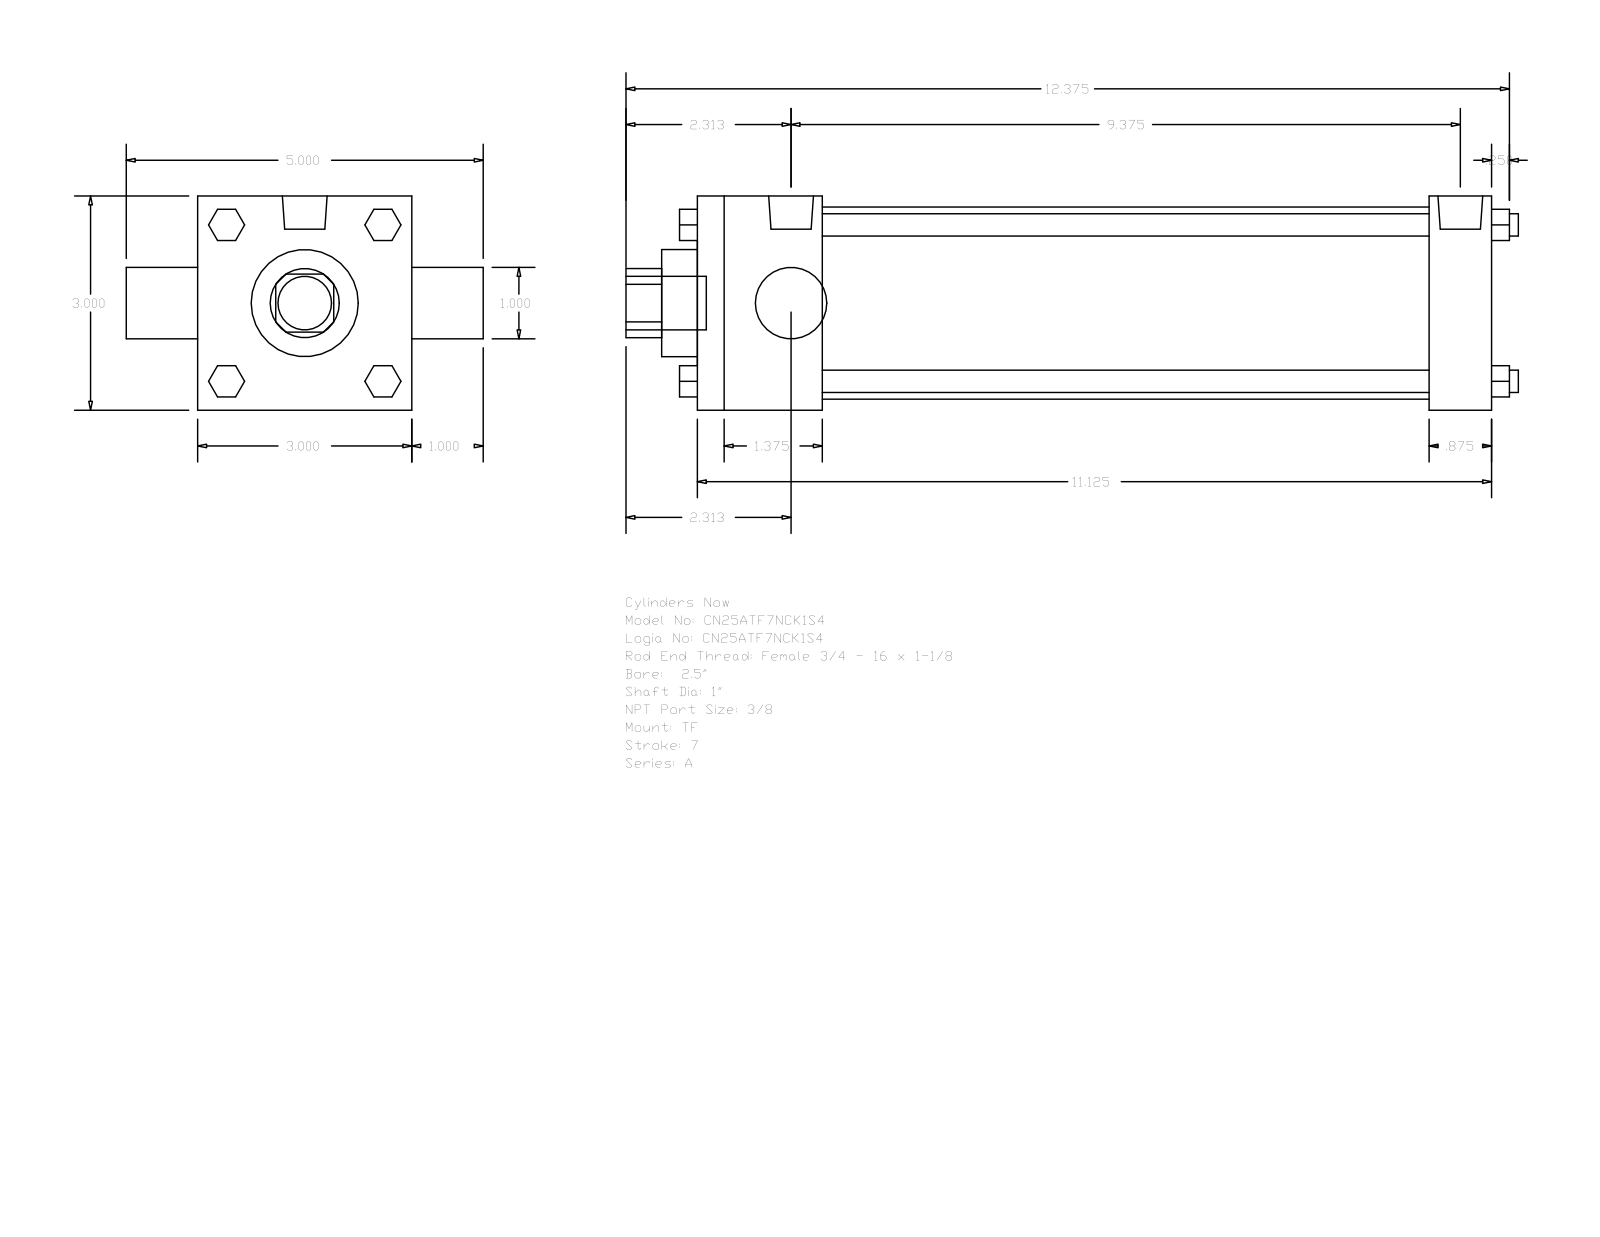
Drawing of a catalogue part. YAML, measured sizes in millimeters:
part_name: "A_TF__0250_1"
step_written_by: "GSSL Pune (CONFIG_CONTROL_DESIGN)"
units: millimeters
bodies: {solids: 0, faces: 120, planar: 92, cylindrical: 28, other: 0}
overall_size: [317.5, 127, 76.2]
round_holes:
  - {diameter: 25.4, count: 2}
  - {diameter: 38.1, count: 1}
  - {diameter: 68.33, count: 1}
round_bosses_or_shafts:
  - {diameter: 7.94, count: 4}
  - {diameter: 5.56, count: 3}
  - {diameter: 15.93, count: 2}
  - {diameter: 19.05, count: 1}
partial_cylinders:
  - {radius: 12.29, count: 1}
face_to_face_distances: [76.2, 282.58, 44.45, 260.35, 215.9, 238.13, 22.23, 25.4, 101.6, 12.7]
